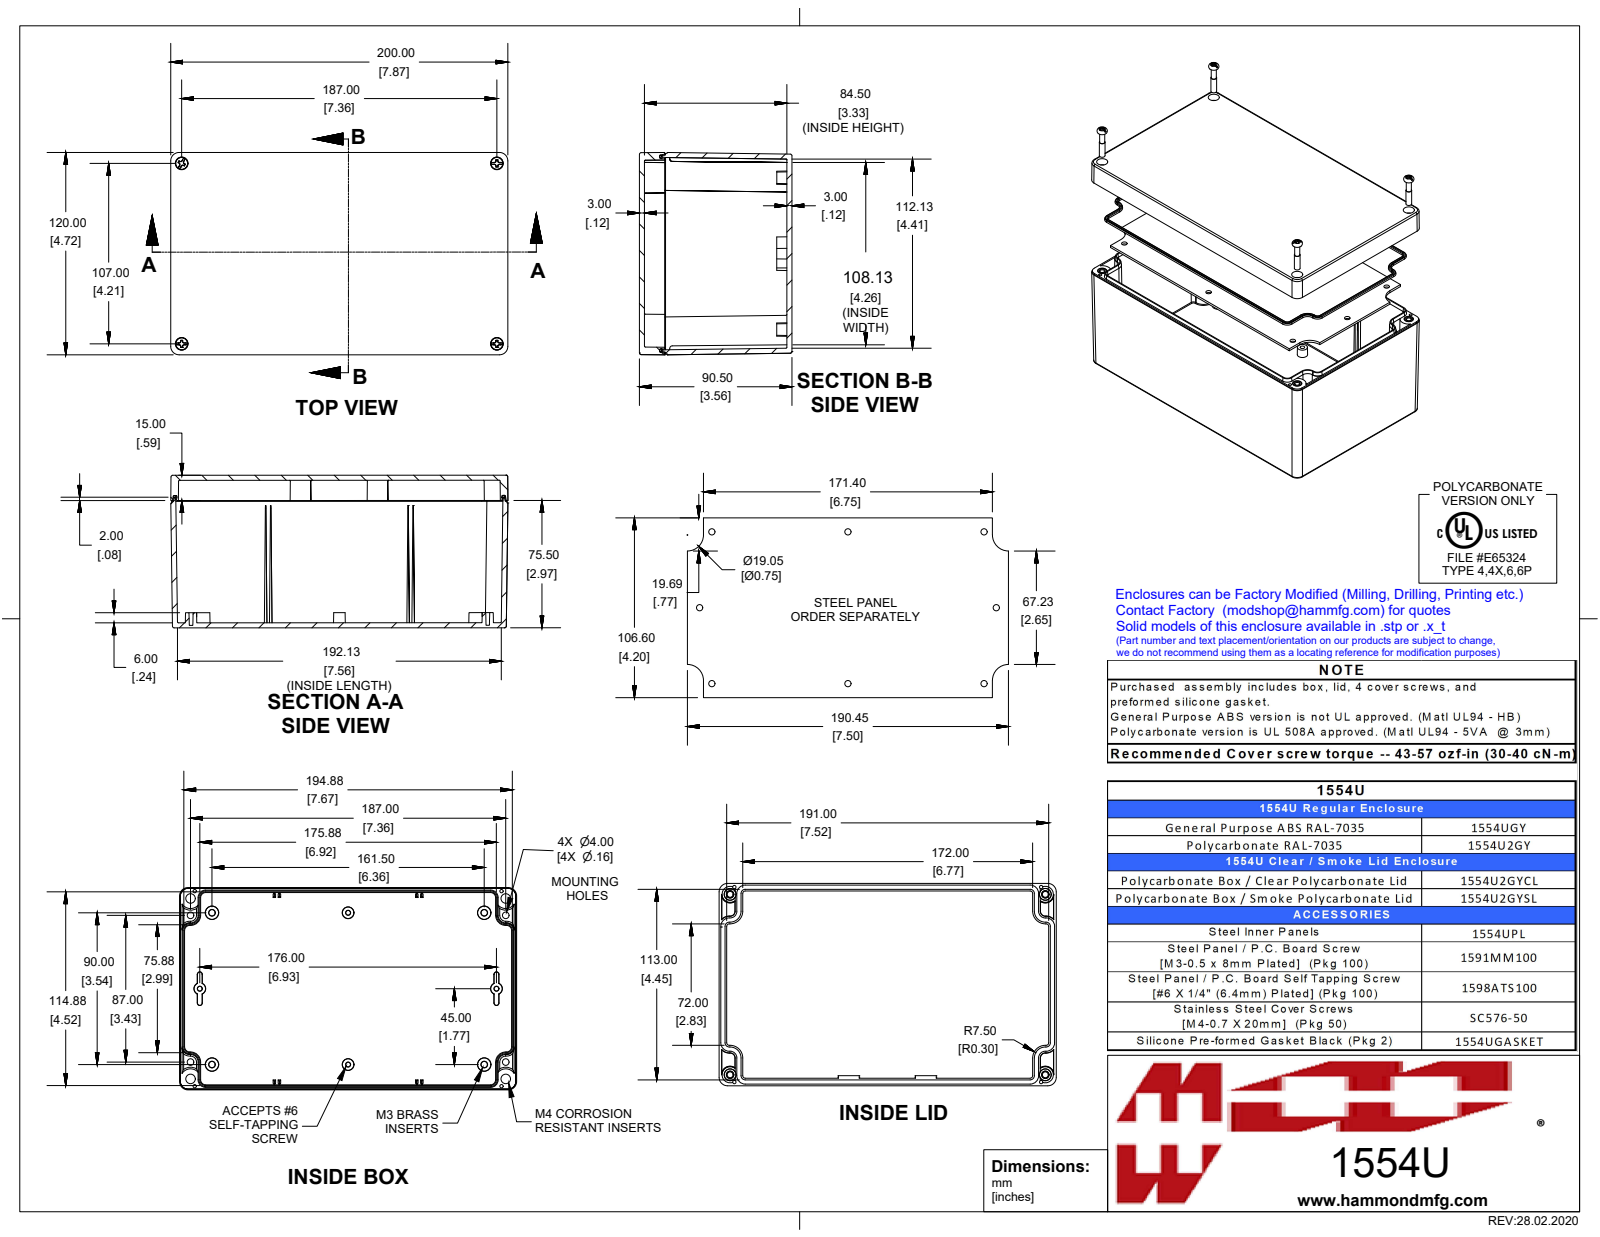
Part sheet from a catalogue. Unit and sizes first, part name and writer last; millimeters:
Units: millimetres
Overall size (bounding box): 200 × 120 × 90.5
Round holes (diameter × count): ⌀2 ×4, ⌀2.5 ×4, ⌀2.8 ×4, ⌀3.3 ×4, ⌀3.5 ×4, ⌀3.7 ×4, ⌀7 ×4
Round bosses / shafts (diameter × count): ⌀6.4 ×4, ⌀5.5 ×4, ⌀5.3 ×4, ⌀4.8 ×4, ⌀3.9 ×4, ⌀3.9 ×4, ⌀3.8 ×4, ⌀3.4 ×4
Partial cylindrical surfaces — rounded edges, fillets, slot ends (radius × count): R0.5 ×52, R1 ×8, R5 ×8, R4.7 ×4, R9.5 ×4, R1.5 ×2
Main face-to-face distances: 3, 87.5, 90.5, 84.5, 9, 78.5, 81.5, 6, 10.6, 7.6
Hole centre spacings: 45.6, 80.7, 99.3, 103.4, 172.2, 174.5, 200.2, 5
Volume: 367 100 mm³ · Surface area: 277 700 mm²
Bodies: 16 solids, 1370 faces (380 planar, 352 cylindrical, 638 other)
Part name (STEP PRODUCT): 1554U2GY
STEP written by: SolidWorks 2019 (AUTOMOTIVE_DESIGN)
